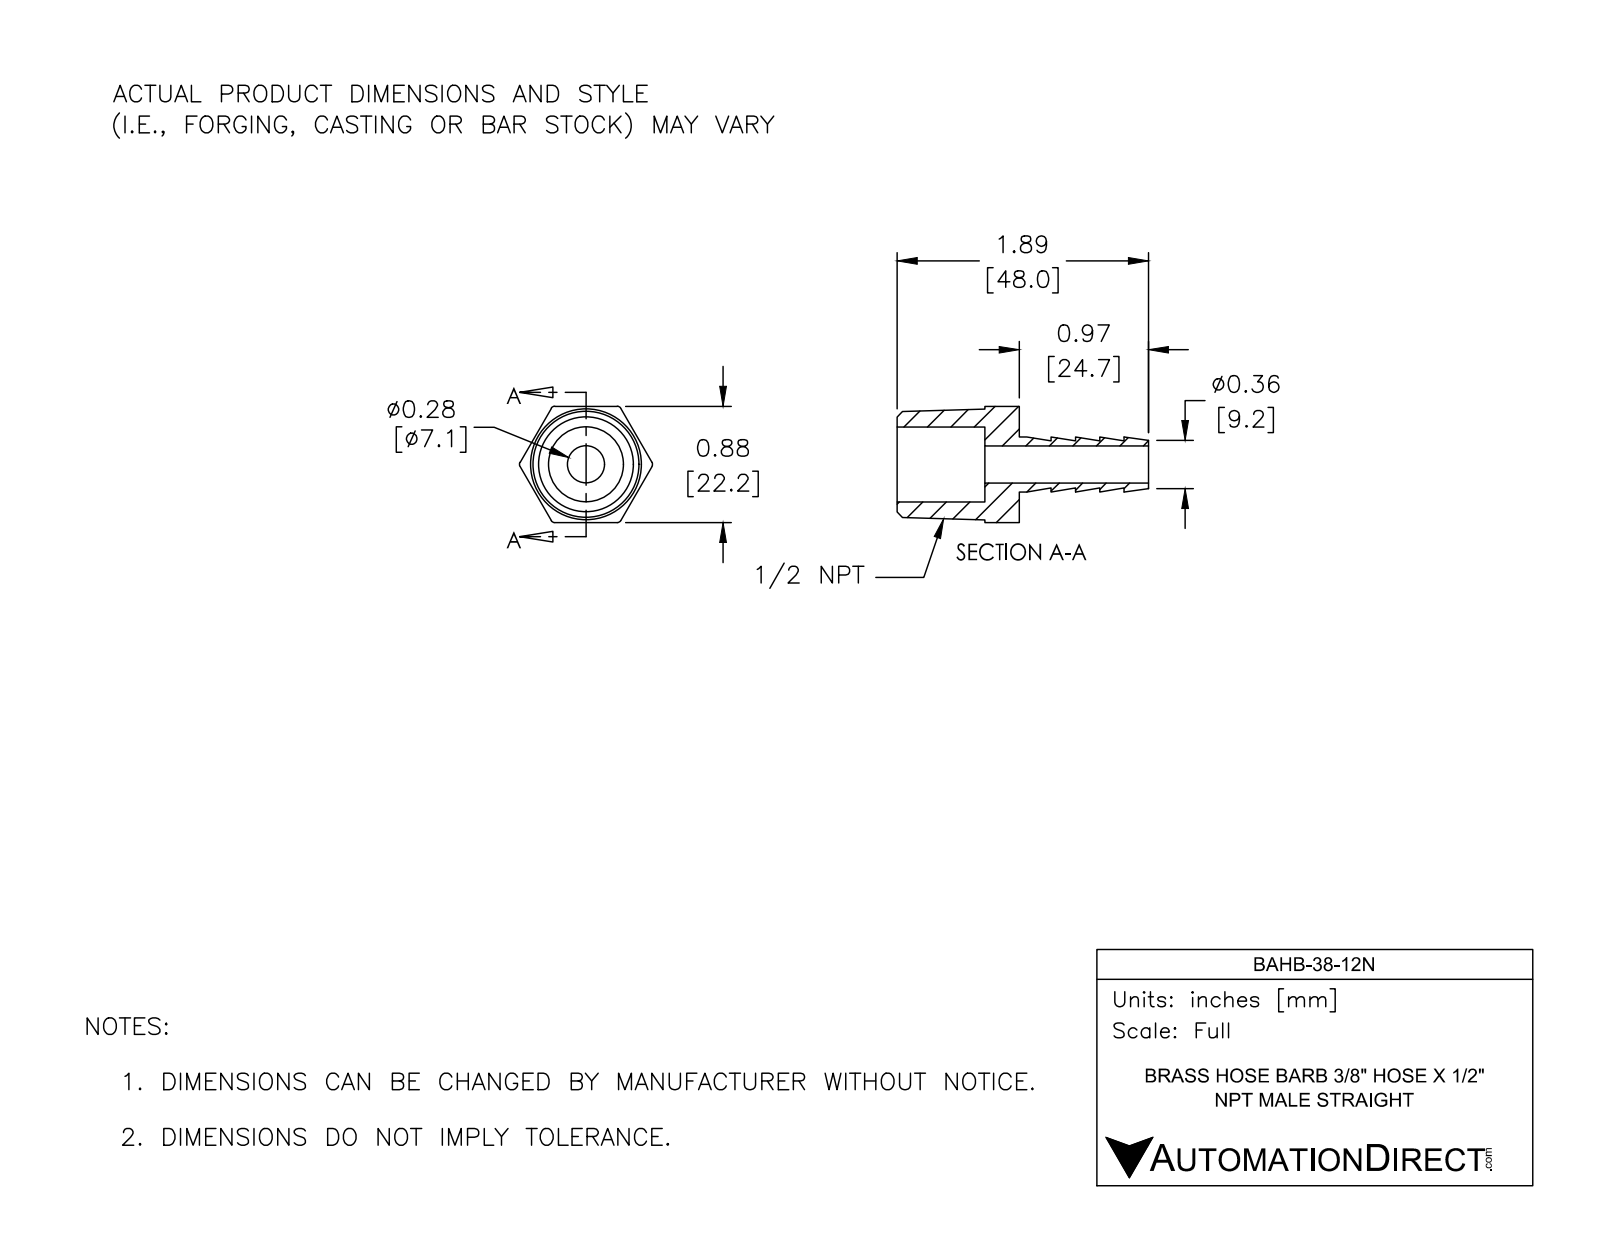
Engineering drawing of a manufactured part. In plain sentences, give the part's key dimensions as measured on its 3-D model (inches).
The part is named "BAHB-38-12N". Its 3-D file was written by "SolidWorks 2017 (AUTOMOTIVE_DESIGN)". It is 1 solid with 41 faces: 15 planar, 12 cylindrical and 14 other. Overall it measures 1.89 by 1.001 by 0.875 inches. Its volume is 0.386 cubic inches and its surface area 7.112 square inches. Round holes: 1 of diameter 0.28, 1 of diameter 0.564. Round bosses or shafts: 1 of diameter 0.414. Partial cylindrical surfaces (rounded edges, fillets, slot ends): 6 of radius 0.03. The main face-to-face distances are 0.875, 0.259, 0.918, 0.659, 0.183, 0.366, 0.972, 1.231, 1.89, 0.549.
